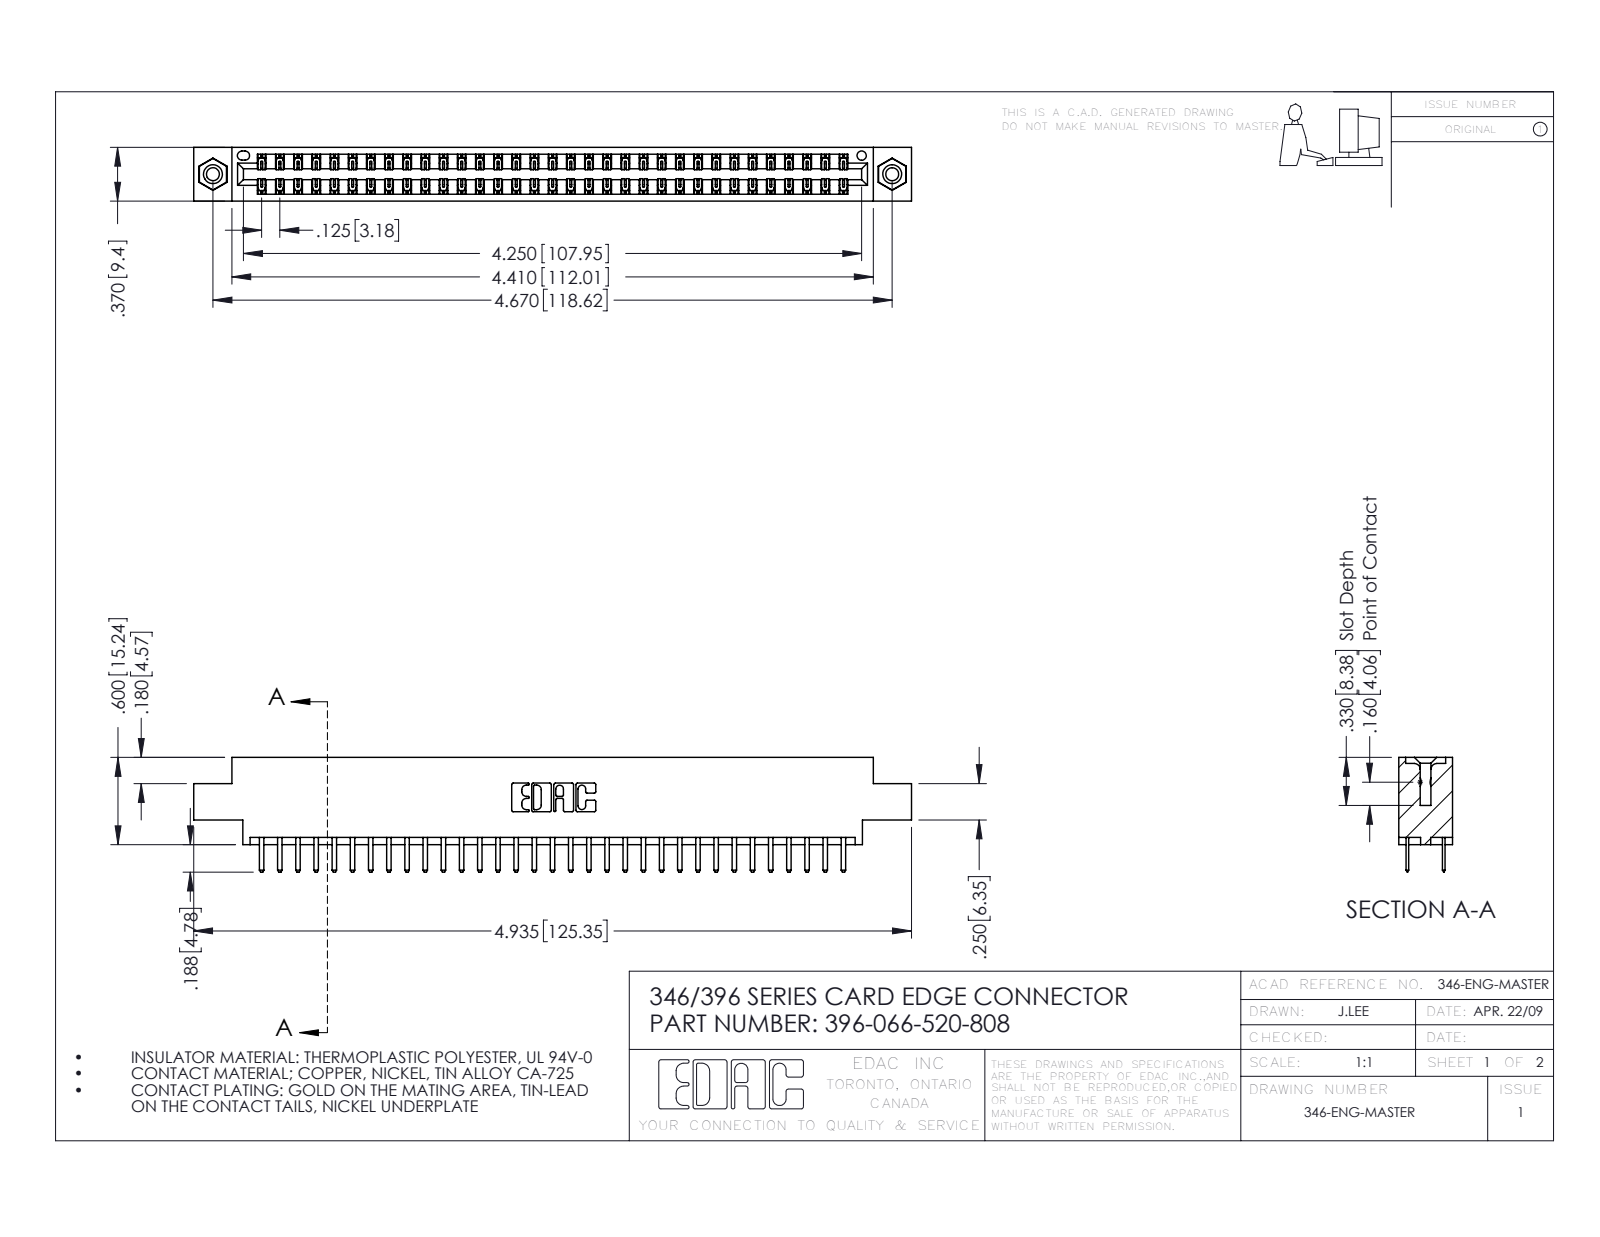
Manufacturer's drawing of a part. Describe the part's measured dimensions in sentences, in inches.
The part is named "345-250-001_345-250-003-102; 346 Part_0.170 Offset - 0.156 Dia-TI; 396-066-520-808; 345-292-001_345-293-120". Its 3-D file was written by "SolidWorks 2016 (CONFIG_CONTROL_DESIGN)". It is 69 solids with 3882 faces: 2554 planar, 1312 cylindrical and 16 other. Overall it measures 4.935 by 0.788 by 0.37 inches. Its volume is 0.73 cubic inches and its surface area 25.47 square inches. Round holes: 2 of diameter 0.089, 2 of diameter 0.125, 2 of diameter 0.156, 1 of diameter 0.064. Round bosses or shafts: 2 of diameter 0.155. Partial cylindrical surfaces (rounded edges, fillets, slot ends): 99 of radius 0.006, 70 of radius 0.01, 22 of radius 0.01, 6 of radius 0.007, 6 of radius 0.031, 3 of radius 0.026, 2 of radius 0.014, 2 of radius 0.022. The main face-to-face distances are 0.048, 0.322, 0.37, 0.25, 0.275, 0.072, 0.298, 0.025, 0.222, 0.148. The hole center spacings are 0.246, 4.462, 4.67.
